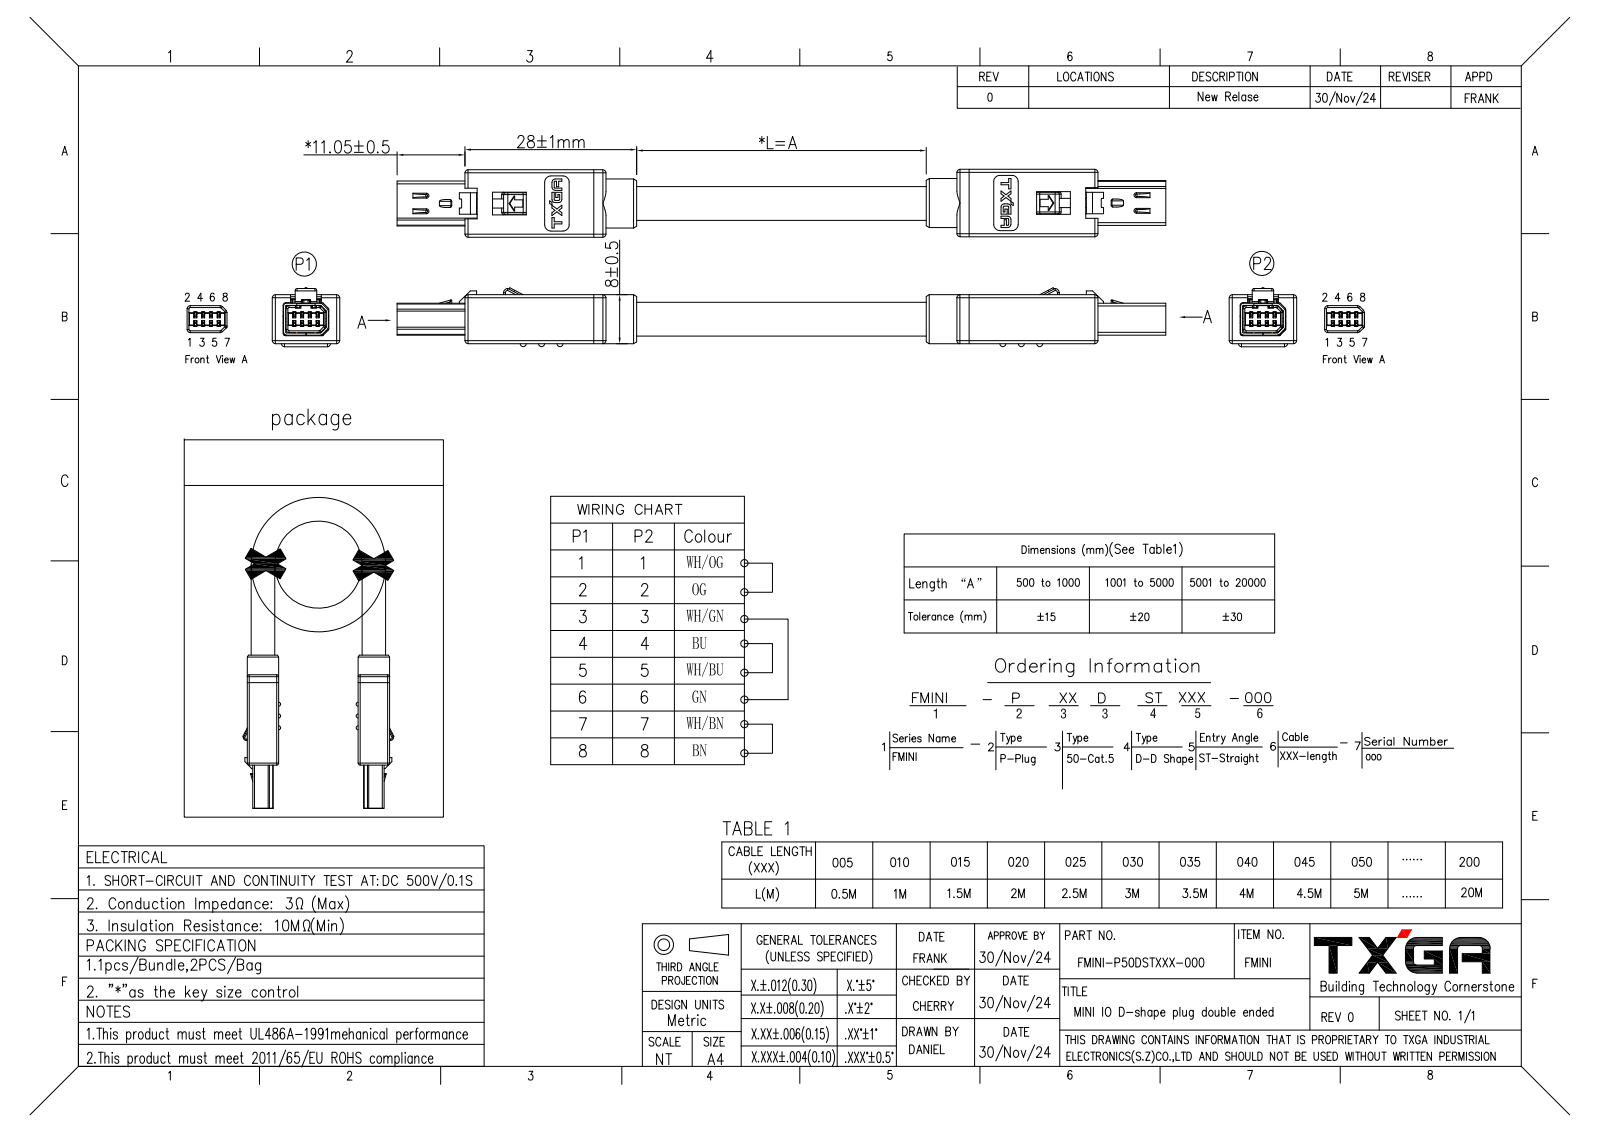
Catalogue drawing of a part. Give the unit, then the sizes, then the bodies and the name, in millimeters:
Units: millimetres
Overall size (bounding box): 110.1 × 11 × 9.62
Round bosses / shafts (diameter × count): ⌀8 ×1, ⌀5 ×1
Partial cylindrical surfaces — rounded edges, fillets, slot ends (radius × count): R0.2 ×110, R0.1 ×76, R0.3 ×68, R0.5 ×60, R0.8 ×40, R0.45 ×38, R0.4 ×20, R1 ×16
Main face-to-face distances: 0.35, 0.65, 1.4, 0.75, 1.75, 4.85, 1, 0.5, 6.25, 6.6
Volume: 4 516 mm³ · Surface area: 9 256 mm²
Bodies: 1 solid, 4546 faces (3024 planar, 1138 cylindrical, 384 other)
Part name (STEP PRODUCT): FMINI-PNDSTXXX-000
STEP written by: PRO/ENGINEER BY PARAMETRIC TECHNOLOGY CORPORATION, 2010280 (CONFIG_CONTROL_DESIGN)
